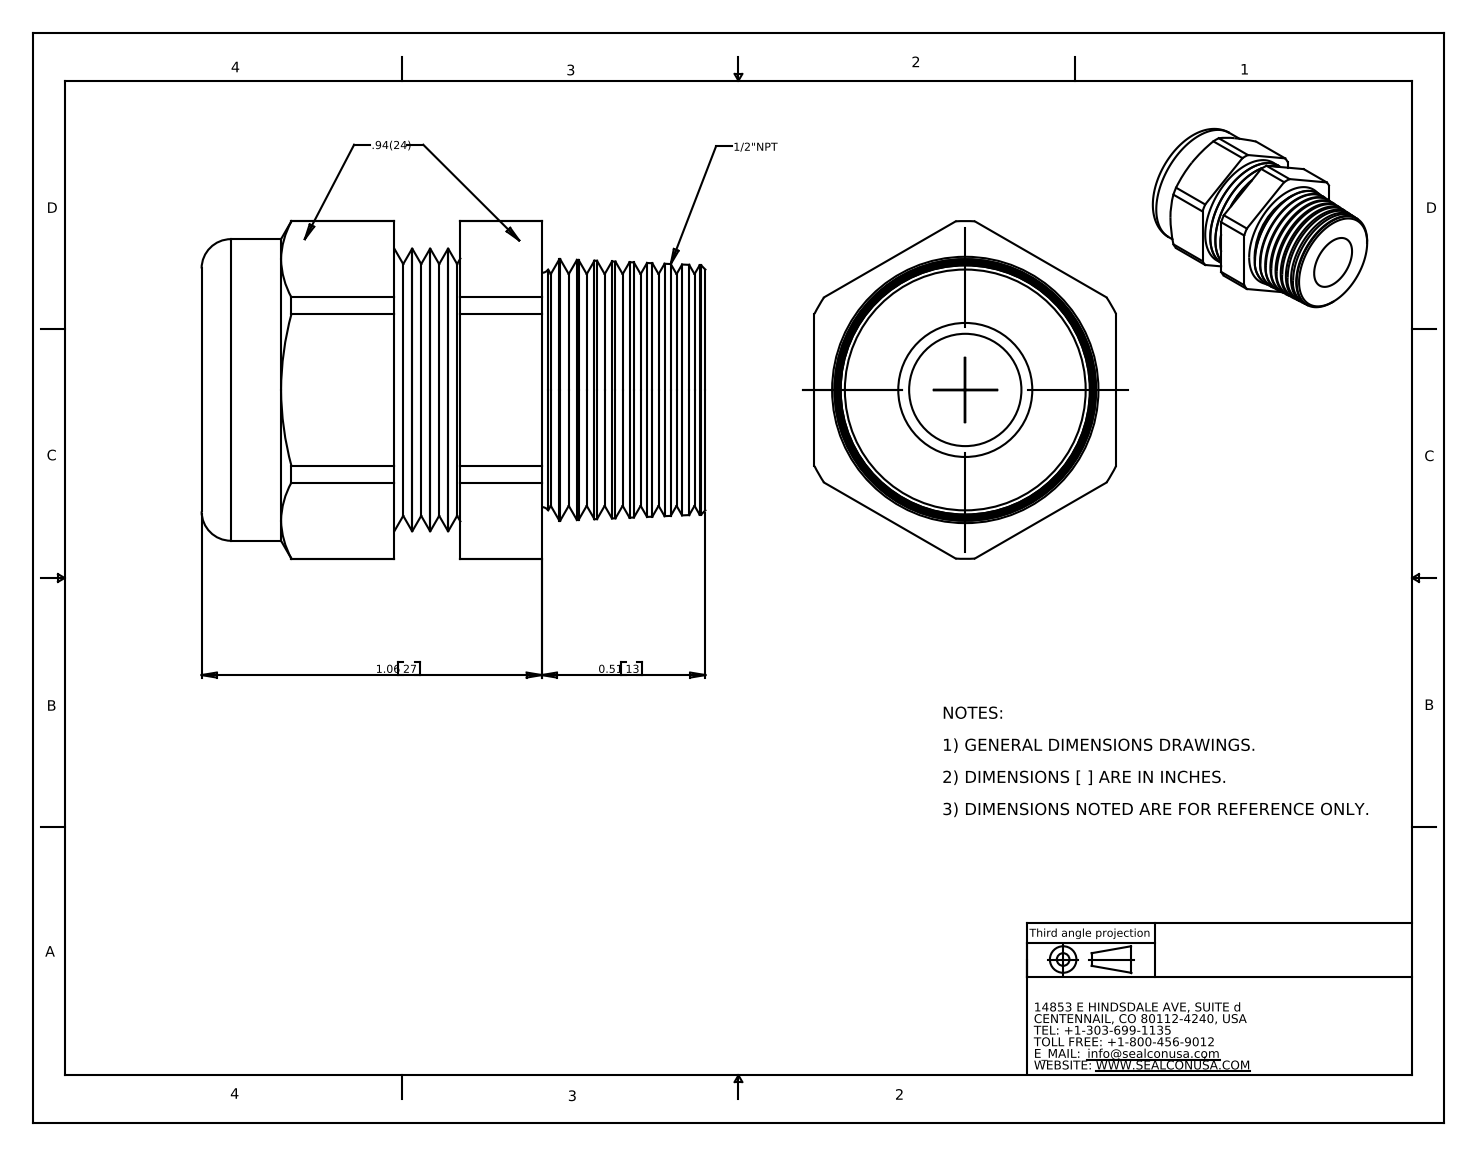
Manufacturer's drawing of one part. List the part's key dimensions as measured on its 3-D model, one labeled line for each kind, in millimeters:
Part name (STEP PRODUCT): CD13NR-GY
STEP written by: SolidWorks 2007 (CONFIG_CONTROL_DESIGN)
Units: millimetres
Bodies: 2 solids, 138 faces (20 planar, 30 cylindrical, 88 other)
Overall size (bounding box): 39.9 × 26.7 × 23.9
Volume: 13 000 mm³ · Surface area: 7 077 mm²
Round holes (diameter × count): ⌀8.9 ×1, ⌀17.7 ×1
Round bosses / shafts (diameter × count): ⌀23.9 ×1, ⌀22.4 ×1
Partial cylindrical surfaces — rounded edges, fillets, slot ends (radius × count): R13.4 ×1
Main face-to-face distances: 23.9, 33.6, 5.8, 39.4, 26.4, 20.7, 13, 14.8, 9, 11.7
